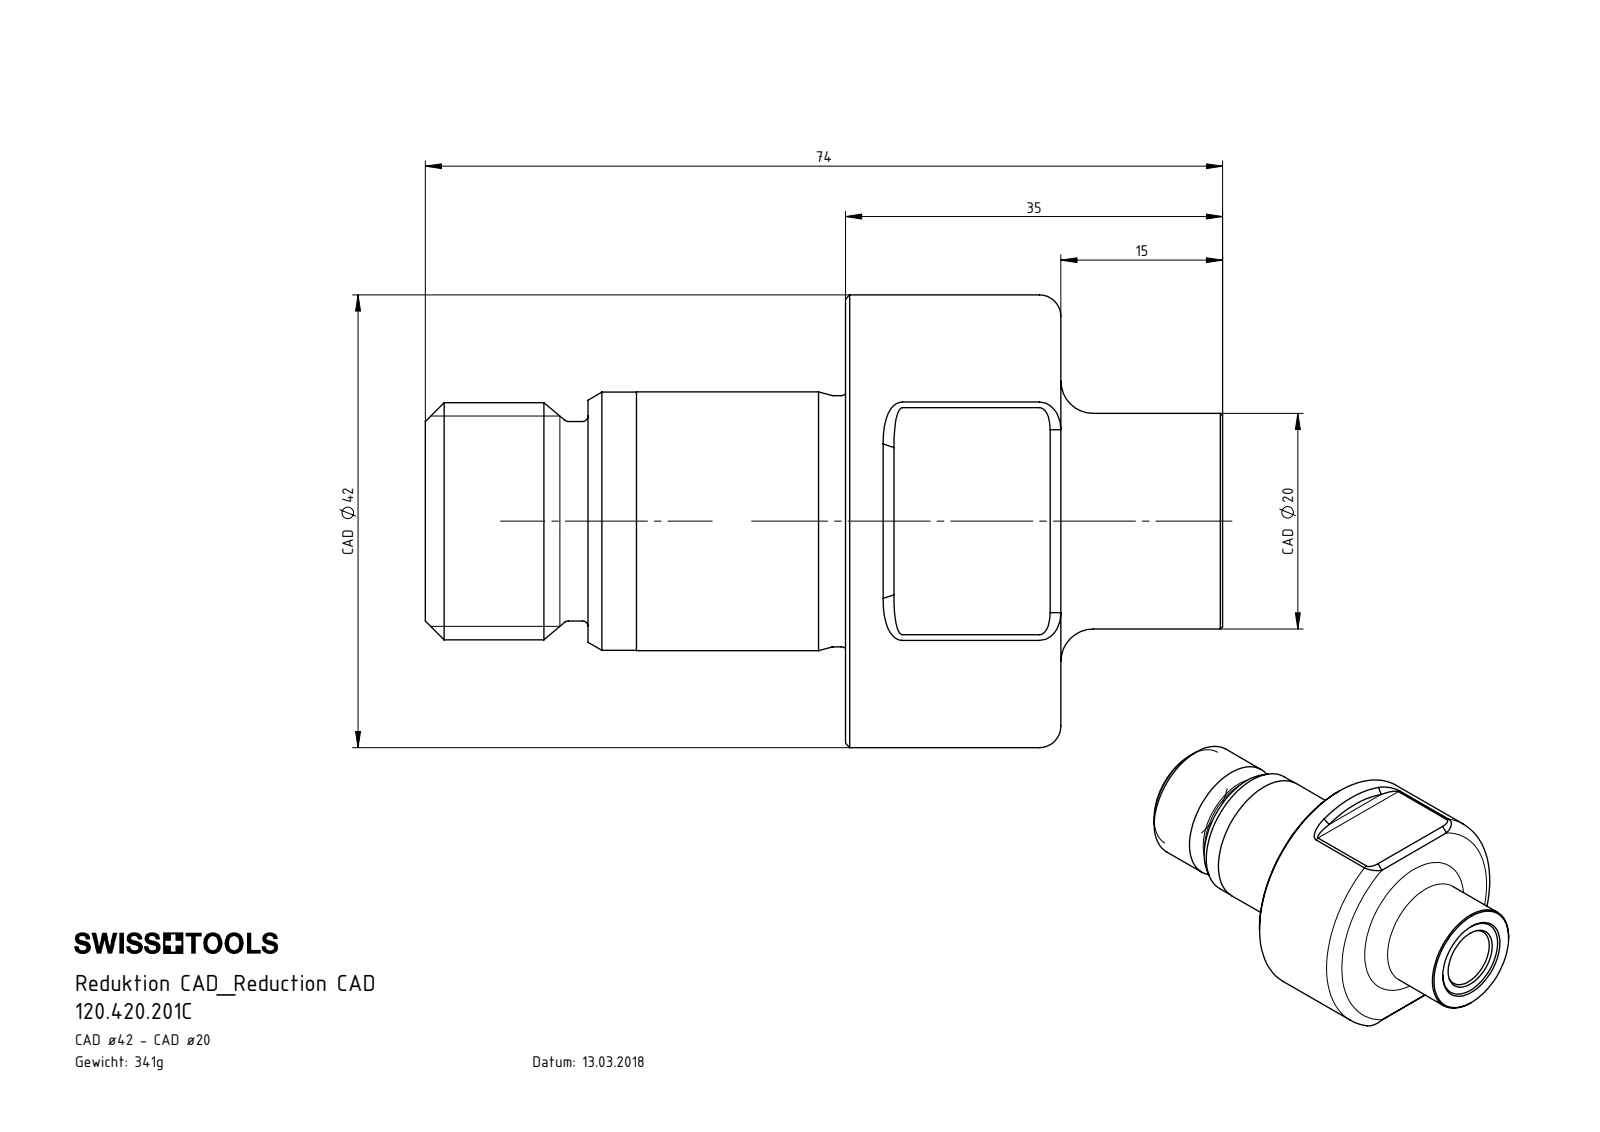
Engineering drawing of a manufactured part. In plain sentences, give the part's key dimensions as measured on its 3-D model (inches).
The part is named "120.420.201C". Its 3-D file was written by "SolidWorks 2017 (CONFIG_CONTROL_DESIGN)". It is 1 solid with 95 faces: 18 planar, 24 cylindrical and 53 other. Overall it measures 2.913 by 1.654 by 1.654 inches. Its volume is 2.647 cubic inches and its surface area 16.45 square inches. Round holes: 1 of diameter 0.268, 1 of diameter 0.335, 1 of diameter 0.433, 1 of diameter 0.453. Round bosses or shafts: 1 of diameter 1.654, 1 of diameter 0.945, 1 of diameter 0.943, 1 of diameter 0.917, 1 of diameter 0.866, 1 of diameter 0.787, 1 of diameter 0.728. Partial cylindrical surfaces (rounded edges, fillets, slot ends): 2 of radius 0.031. The main face-to-face distances are 0.787, 1.417, 1.535, 2.323, 2.913, 1.378, 0.591, 0.941, 0.594, 1.728.
